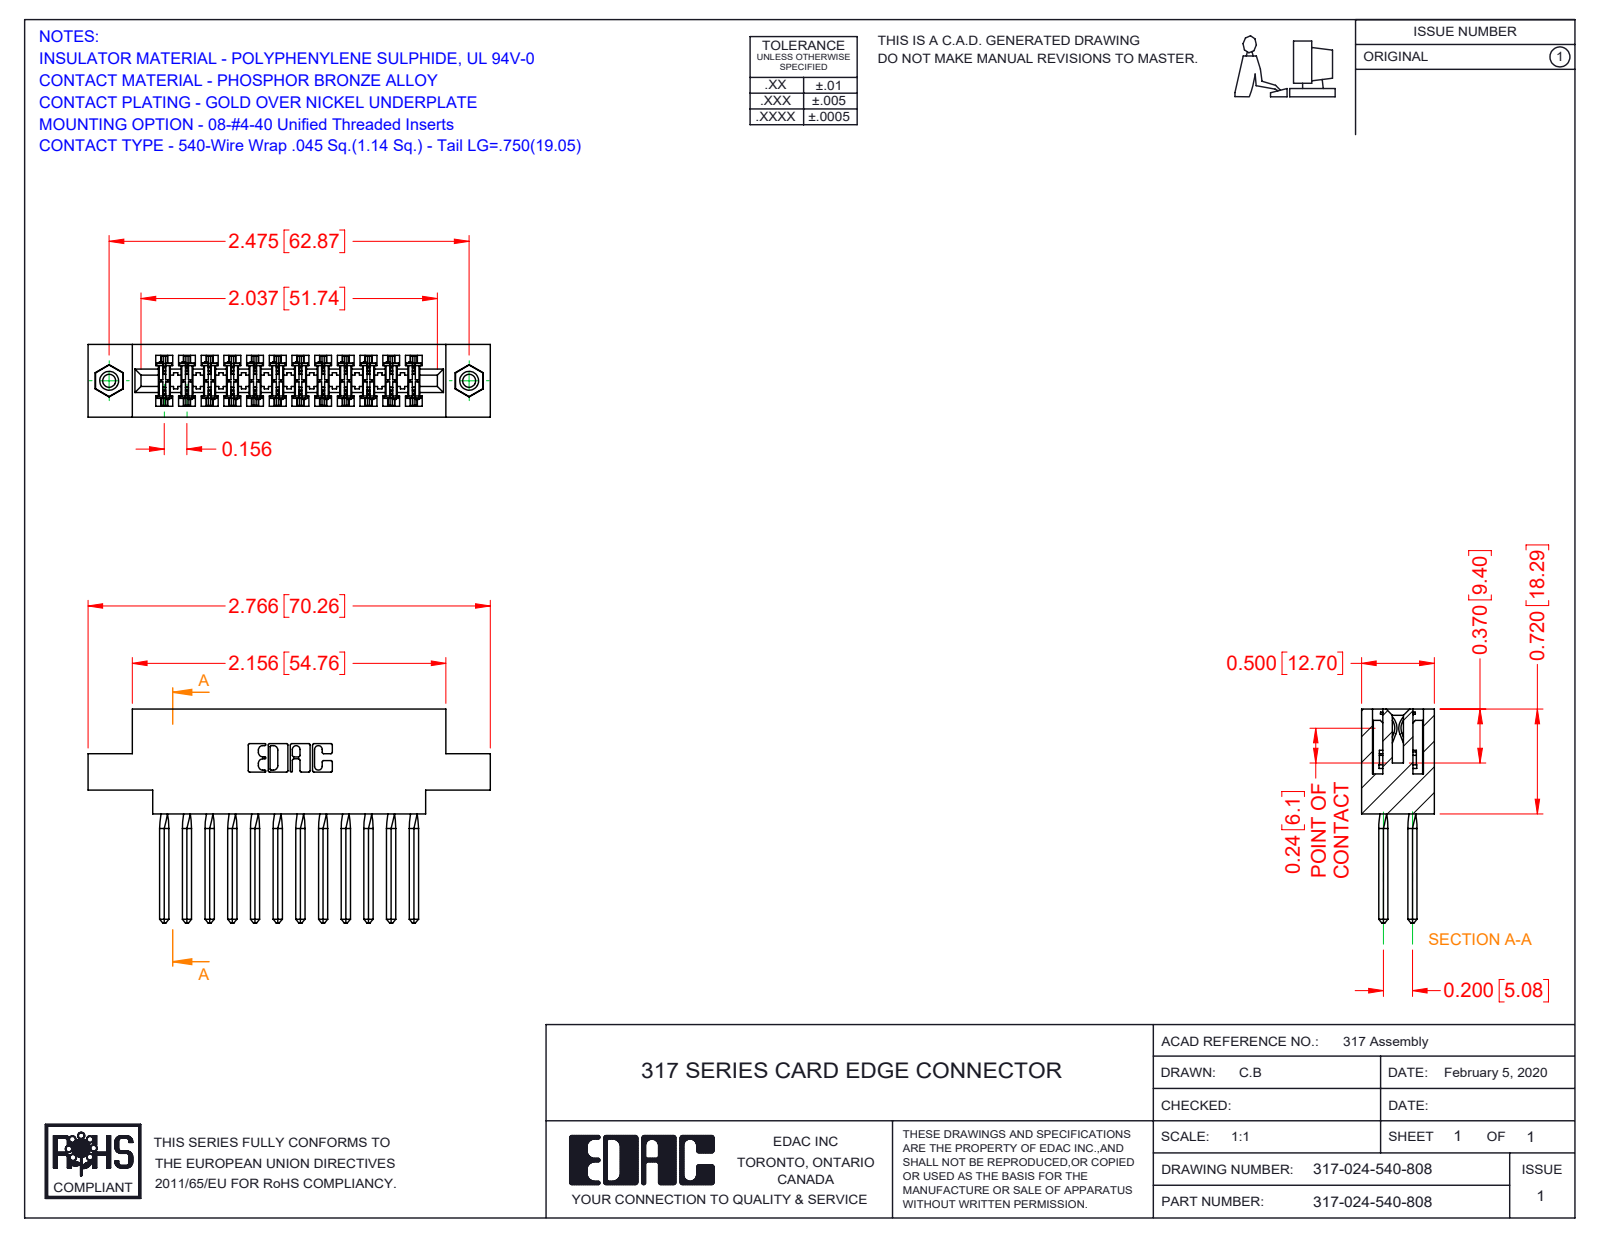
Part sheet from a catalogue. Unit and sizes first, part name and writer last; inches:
Units: inches
Overall size (bounding box): 2.766 × 1.47 × 0.5
Round holes (diameter × count): ⌀0.089 ×2, ⌀0.125 ×2, ⌀0.156 ×2
Round bosses / shafts (diameter × count): ⌀0.155 ×2
Partial cylindrical surfaces — rounded edges, fillets, slot ends (radius × count): R0.015 ×48, R0.01 ×22, R0.007 ×6, R0.031 ×6, R0.026 ×3, R0.095 ×2, R0.1 ×2, R0.11 ×2
Main face-to-face distances: 0.5, 0.075, 0.425, 0.11, 0.22, 0.35, 0.331, 0.136, 0.156, 0.305
Hole centre spacings: 2.475
Volume: 0.657 in³ · Surface area: 23.17 in²
Bodies: 27 solids, 2298 faces (1842 planar, 344 cylindrical, 112 other)
Part name (STEP PRODUCT): 317-024-540-808; 317-290-001_540; 345-250-001_345-250-003-102; 317 Part_.156 Dia - TI
STEP written by: SolidWorks 2016 (CONFIG_CONTROL_DESIGN)
